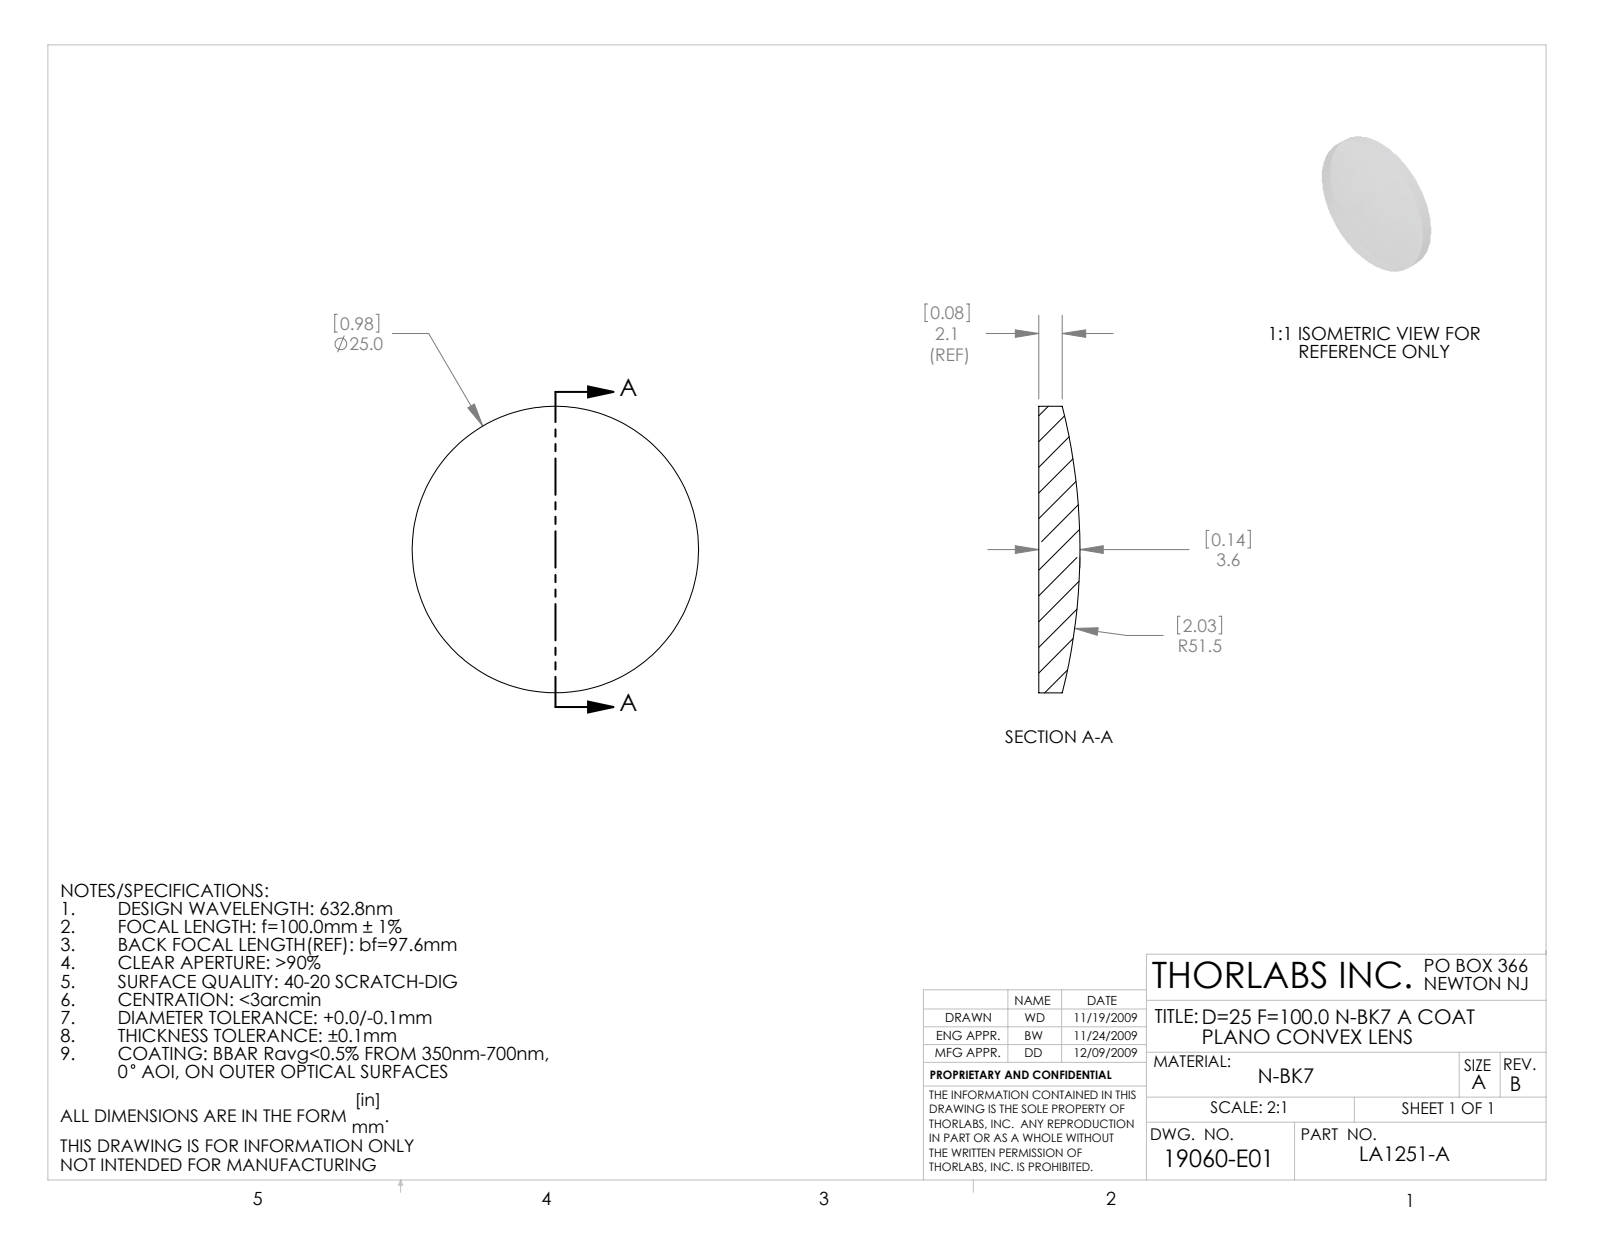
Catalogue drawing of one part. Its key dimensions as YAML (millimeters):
part_name: "19060-E0W"
step_written_by: "SolidWorks 2009 (AUTOMOTIVE_DESIGN)"
units: millimeters
bodies: {solids: 1, faces: 5, planar: 1, cylindrical: 2, other: 2}
overall_size: [25, 25, 3.6]
volume: 1391
surface_area: 1151
round_bosses_or_shafts:
  - {diameter: 25, count: 1}
